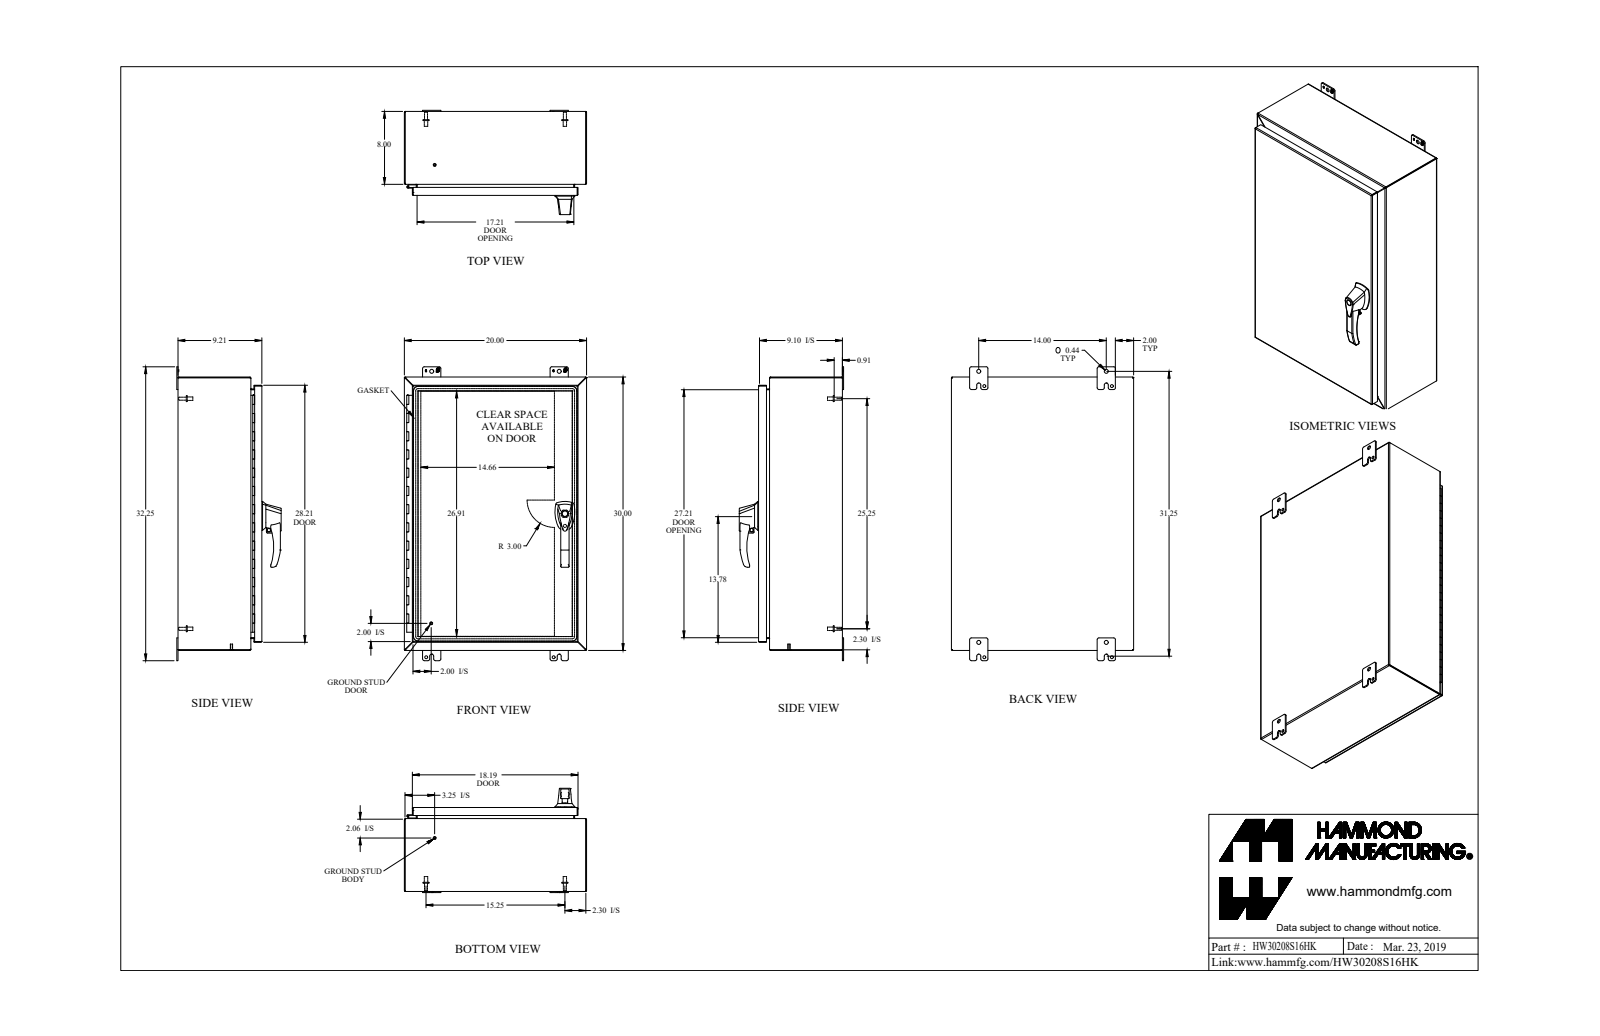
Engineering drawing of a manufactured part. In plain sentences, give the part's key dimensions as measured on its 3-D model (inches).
The part is named "HW30208S16HK". Its 3-D file was written by "SolidWorks 2018 (AUTOMOTIVE_DESIGN)". It is 42 solids with 1474 faces: 709 planar, 613 cylindrical and 152 other. Overall it measures 32.25 by 20 by 11.45 inches. Its volume is 194.4 cubic inches and its surface area 4 998 square inches. Round holes: 6 of diameter 0.176, 5 of diameter 0.313, 3 of diameter 0.25, 3 of diameter 0.265, 3 of diameter 0.413, 2 of diameter 0.196, 2 of diameter 0.256, 2 of diameter 0.394, 2 of diameter 0.437, 1 of diameter 0.11, 1 of diameter 0.233, 1 of diameter 0.33. Round bosses or shafts: 9 of diameter 0.375, 7 of diameter 0.25, 6 of diameter 0.156, 4 of diameter 0.65, 4 of diameter 0.332, 4 of diameter 0.313, 3 of diameter 1, 3 of diameter 0.51. Partial cylindrical surfaces (rounded edges, fillets, slot ends): 27 of radius 0.25, 24 of radius 0.188, 20 of radius 0.036, 20 of radius 0.108, 12 of radius 0.06, 9 of radius 0.125, 8 of radius 0.045, 8 of radius 0.218. The main face-to-face distances are 0.072, 9.138, 9.066, 0.072, 9.138, 9.21, 19.928, 29.928, 7.928, 19.856. The hole center spacings are 1.111, 11.118, 11.119, 22.237, 1.338, 9.78, 10.563, 10.565.
